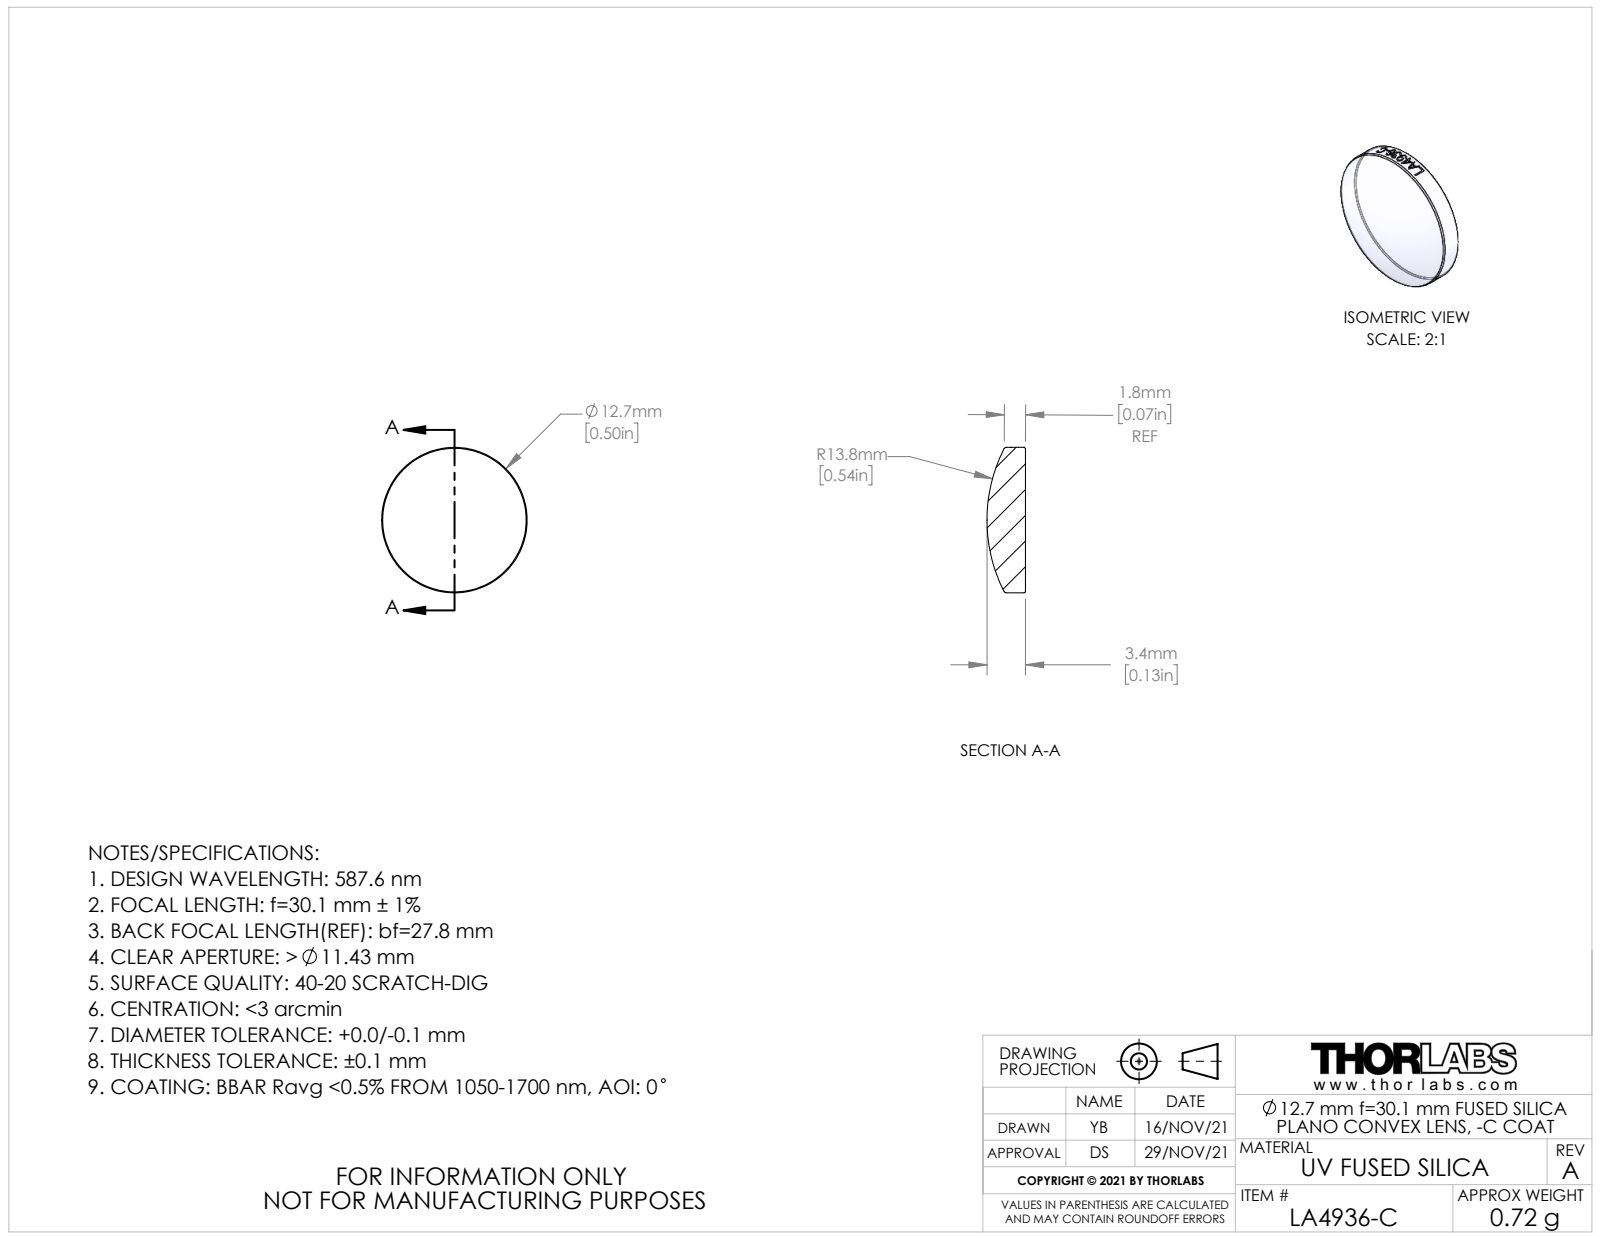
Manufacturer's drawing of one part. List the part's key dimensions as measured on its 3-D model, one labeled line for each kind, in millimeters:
Part name (STEP PRODUCT): CTN018064-E0W; CTN018133
STEP written by: SolidWorks 2018 (AUTOMOTIVE_DESIGN)
Units: millimetres
Bodies: 1 solid, 21 faces (1 planar, 14 cylindrical, 6 other)
Overall size (bounding box): 12.7 × 12.7 × 3.35
Volume: 328 mm³ · Surface area: 329 mm²
Round bosses / shafts (diameter × count): ⌀12.7 ×1
